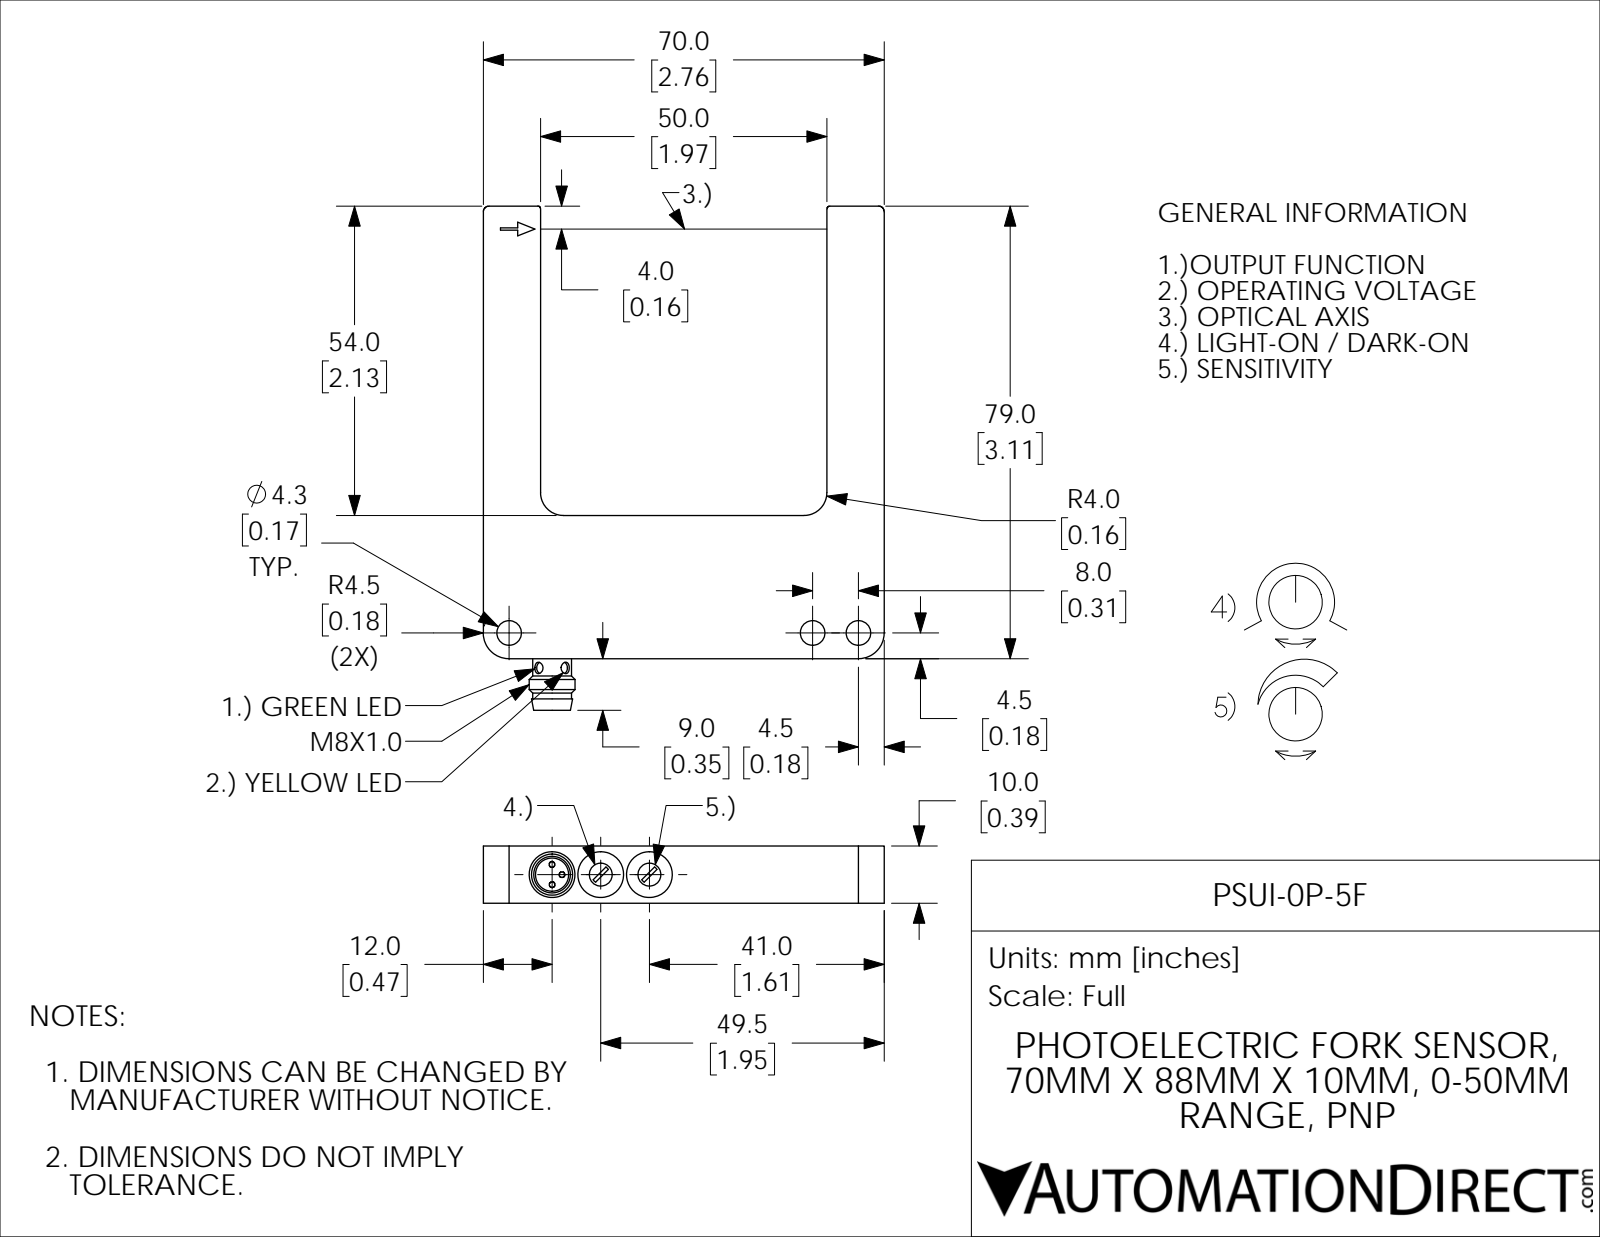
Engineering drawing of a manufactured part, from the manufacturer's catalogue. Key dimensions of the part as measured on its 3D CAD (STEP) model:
Part name (STEP PRODUCT): PSUI-0P-5F
STEP written by: SolidWorks 2017 (AUTOMOTIVE_DESIGN)
Units: inches
Bodies: 1 solid, 71 faces (35 planar, 30 cylindrical, 6 other)
Overall size (bounding box): 3.465 × 2.756 × 0.394
Volume: 1.712 in³ · Surface area: 16 in²
Round holes (diameter × count): ⌀0.169 ×3, ⌀0.079 ×2, ⌀0.157 ×2, ⌀0.315 ×2, ⌀0.228 ×1
Round bosses / shafts (diameter × count): ⌀0.039 ×3, ⌀0.315 ×1, ⌀0.267 ×1
Partial cylindrical surfaces — rounded edges, fillets, slot ends (radius × count): R0.02 ×2, R0.039 ×2, R0.063 ×2, R0.157 ×2, R0.177 ×2
Main face-to-face distances: 0.394, 2.362, 2.756, 1.969, 0.984, 2.126, 3.11, 3.106, 0.98, 0.157
Hole centre spacings: 0.335, 0.315, 0.669, 2.087, 2.402
